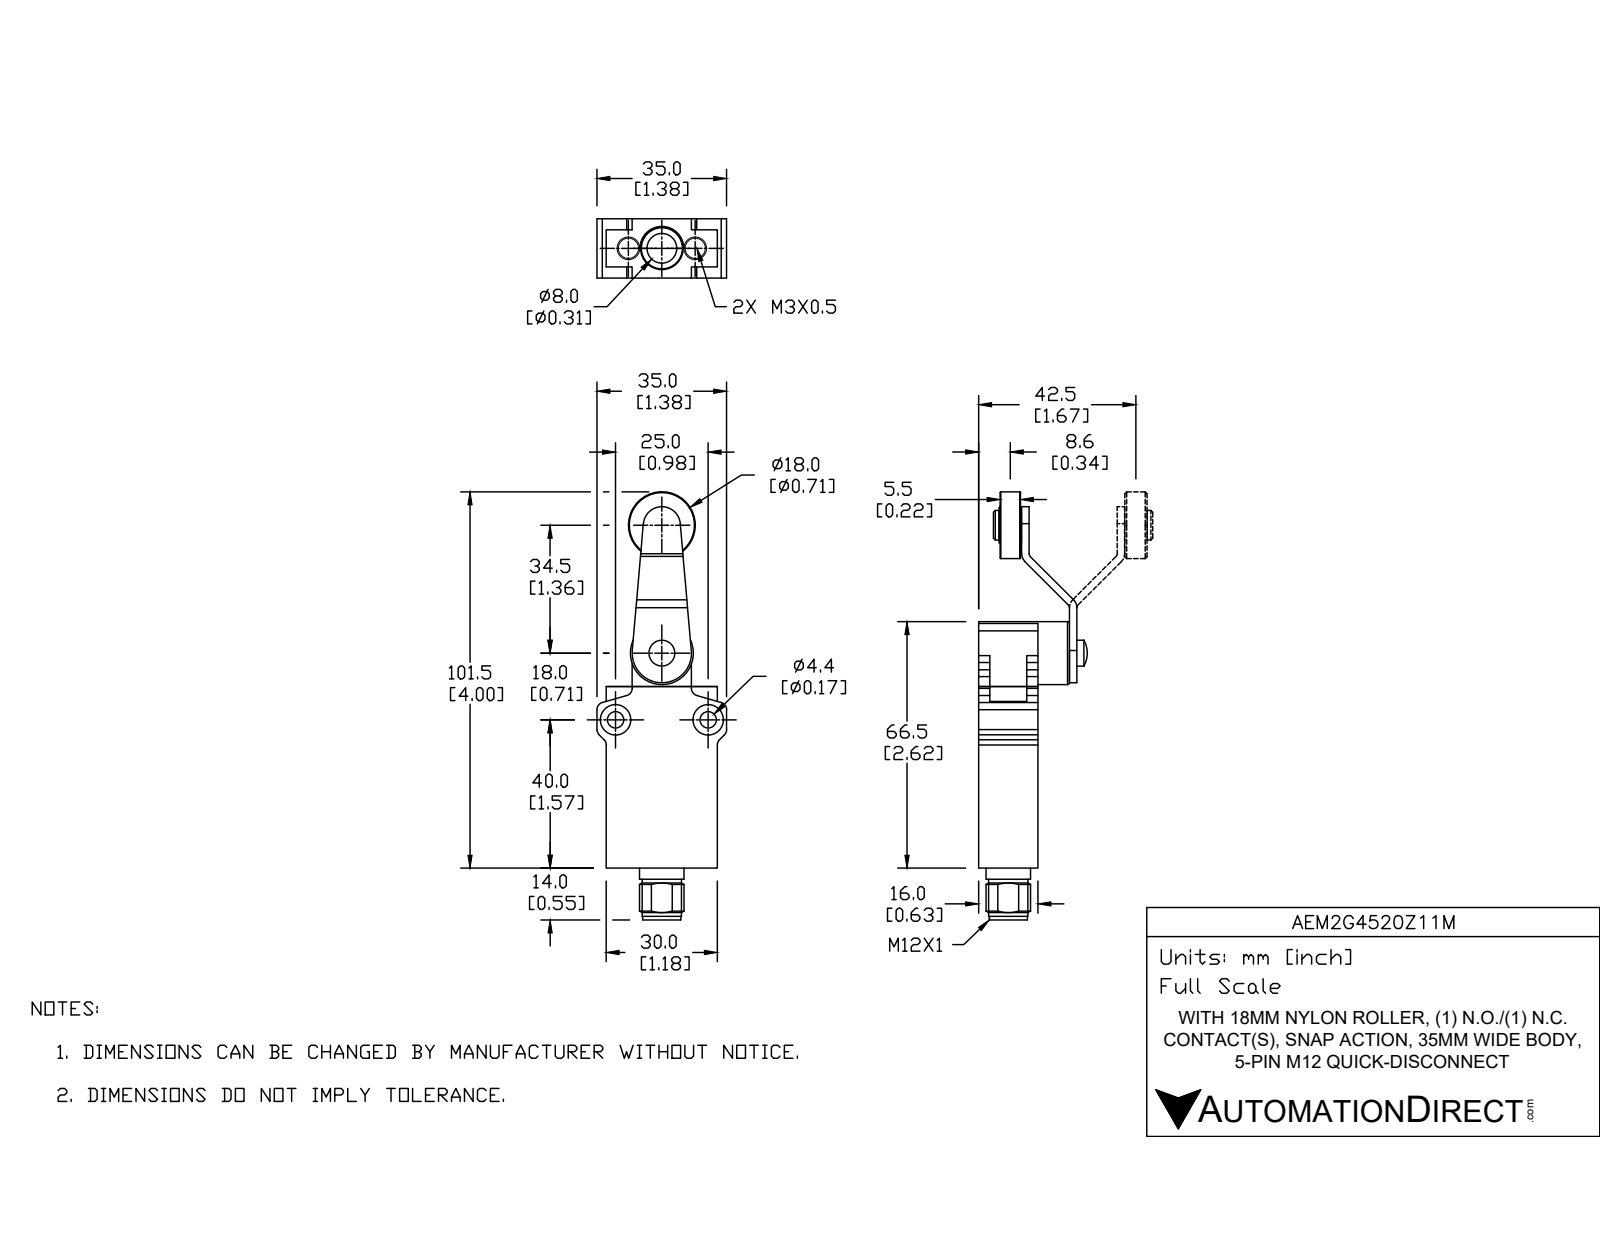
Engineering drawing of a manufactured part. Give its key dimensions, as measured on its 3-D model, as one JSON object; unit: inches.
{"part_name": "AEM2G4520Z11M", "step_written_by": "SolidWorks 2017 (AUTOMOTIVE_DESIGN)", "units": "inches", "bodies": {"solids": 6, "faces": 621, "planar": 300, "cylindrical": 92, "other": 229}, "overall_size": [4.665, 1.378, 1.173], "volume_in3": 2.015, "surface_area_in2": 19.8, "round_holes": [[0.118, 2], [0.173, 2], [0.323, 2], [0.098, 1], [0.138, 1], [0.161, 1], [0.197, 1], [0.224, 1], [0.24, 1]], "round_bosses_or_shafts": [[0.709, 1], [0.622, 1], [0.472, 1], [0.417, 1], [0.406, 1], [0.394, 1], [0.276, 1], [0.236, 1]], "partial_cylinders_radius": [[0.079, 8], [0.039, 5], [0.118, 2], [0.256, 1], [0.315, 1]], "face_to_face_distances": [0.63, 0.079, 1.181, 0.354, 2.047, 0.098, 0.984, 0.472, 0.906, 0.157], "hole_center_spacings": [0.748, 0.861, 0.865, 0.984, 1.358, 2.124, 2.126]}
